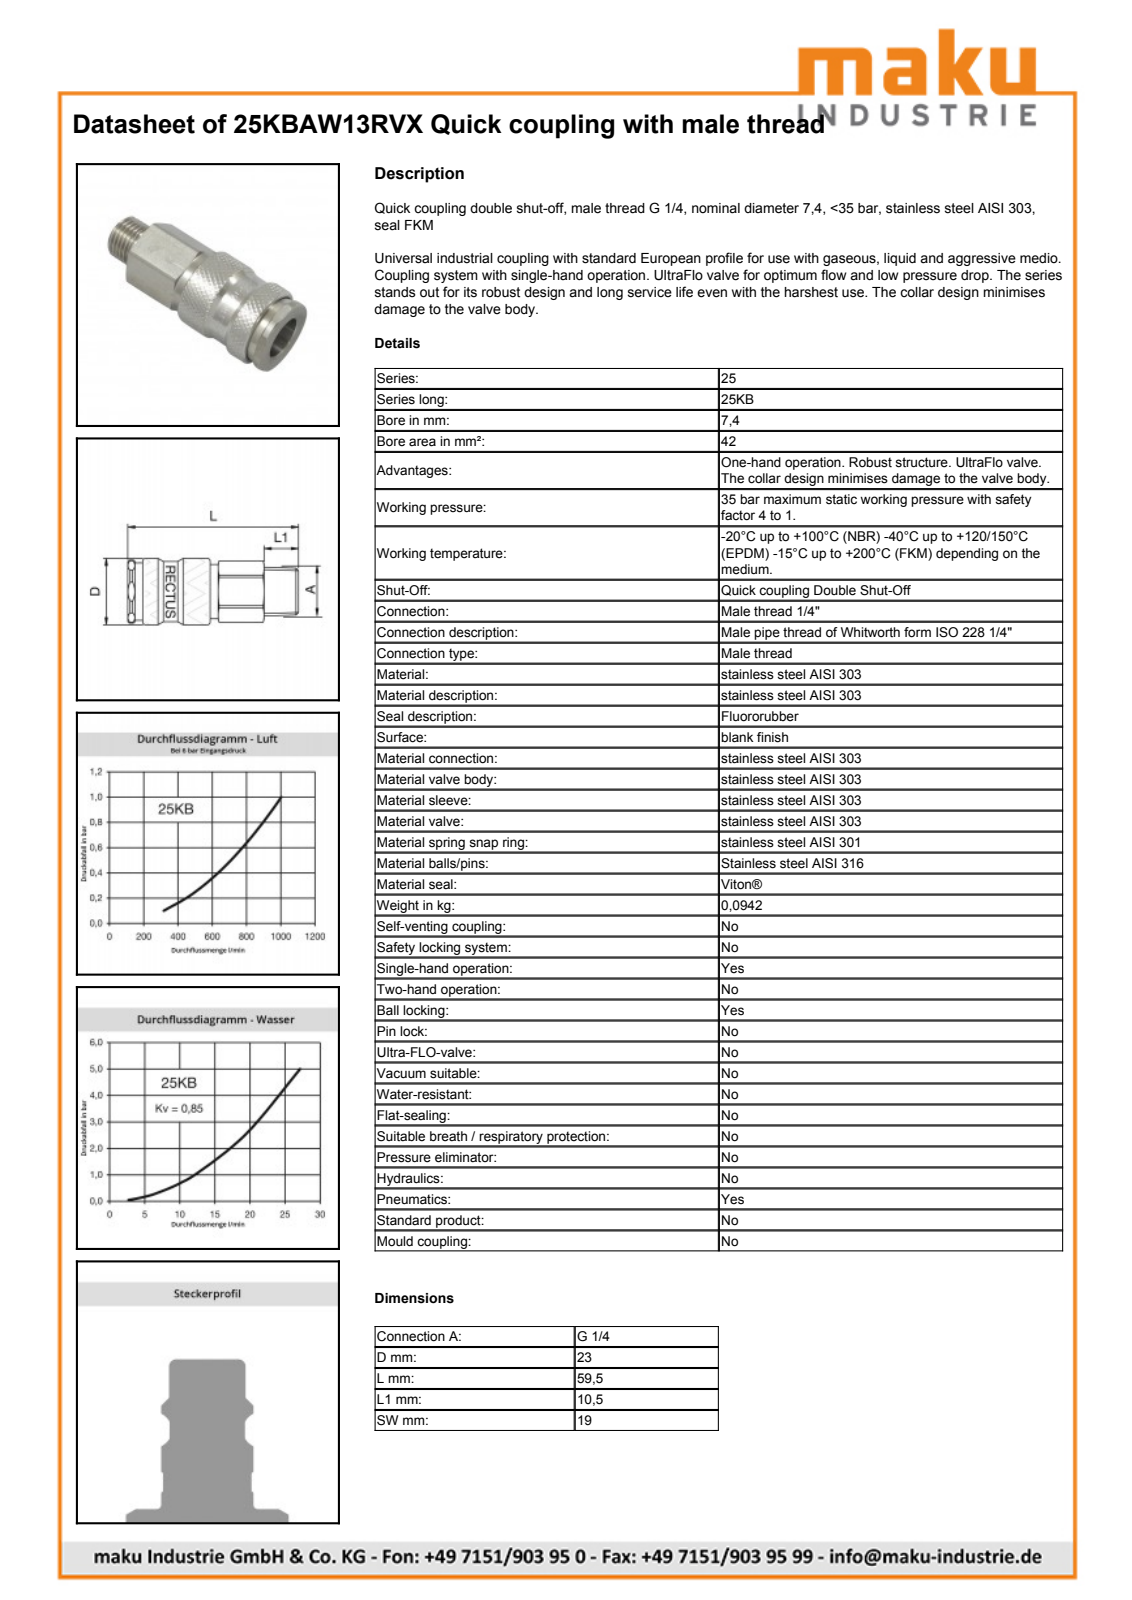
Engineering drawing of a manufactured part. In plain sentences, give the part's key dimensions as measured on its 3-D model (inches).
The part is named "D111975". Its 3-D file was written by "Autodesk Inventor 2013 (AUTOMOTIVE_DESIGN)". It is 2 solids with 616 faces: 213 planar, 79 cylindrical and 324 other. Overall it measures 2.343 by 0.911 by 0.911 inches. Its volume is 1.054 cubic inches and its surface area 12.53 square inches. Round holes: 1 of diameter 0.594, 1 of diameter 0.63, 1 of diameter 0.679, 1 of diameter 0.762, 1 of diameter 0.789. Round bosses or shafts: 1 of diameter 0.911, 1 of diameter 0.827, 1 of diameter 0.787, 1 of diameter 0.746, 1 of diameter 0.669, 1 of diameter 0.602, 1 of diameter 0.591, 1 of diameter 0.518. Partial cylindrical surfaces (rounded edges, fillets, slot ends): 1 of radius 0.409, 1 of radius 0.421, 1 of radius 0.433. The main face-to-face distances are 0.748, 0.965, 2.343, 0.413, 1.929, 0.039, 0.787, 1.378, 0.207, 0.758.
